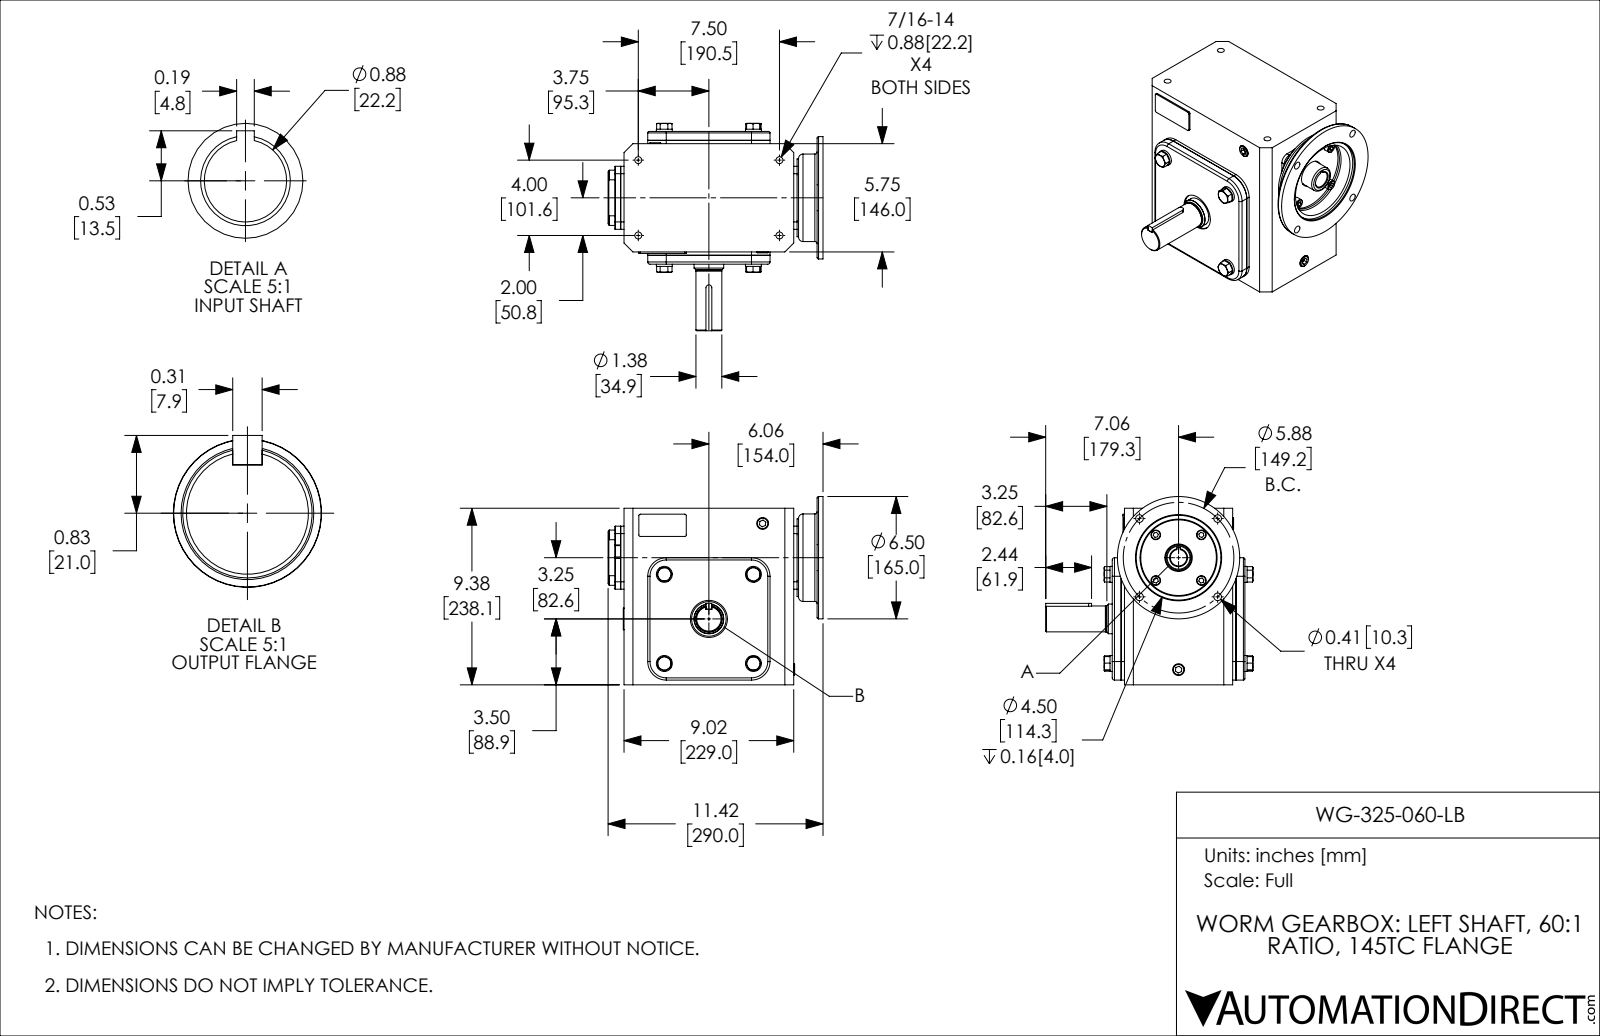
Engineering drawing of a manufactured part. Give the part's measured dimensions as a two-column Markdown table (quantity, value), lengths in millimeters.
| quantity | value |
| --- | --- |
| part name | WG-325-060-LB |
| STEP written by | SolidWorks 2017 (AUTOMOTIVE_DESIGN) |
| units | millimeters |
| bodies | 39 solids, 575 faces (318 planar, 167 cylindrical, 90 other) |
| overall size | 290 × 279.8 × 253.9 |
| volume | 8 259 000 mm³ |
| surface area | 582 200 mm² |
| round holes (diameter × count) | 9.3 × 4, 10.3 × 4, 16 × 3, 15 × 1, 22.2 × 1, 24.8 × 1, 30 × 1, 37 × 1, 50 × 1, 62 × 1, 70 × 1, 102 × 1 |
| round bosses / shafts (diameter × count) | 21.5 × 4, 13 × 4, 165 × 1, 118 × 1, 105 × 1, 72 × 1, 40 × 1, 35 × 1 |
| partial cylindrical surfaces (radius × count) | 2 × 11, 3 × 4, 10 × 4, 23 × 4, 25 × 4, 0.5 × 2, 1 × 2, 4 × 1 |
| main face-to-face distances | 2, 4.5, 165, 10, 177, 12, 167, 162.5, 14.5, 16.5 |
| hole center spacings | 74.6, 105.5, 60.6, 101.6, 111.5, 145.2, 147.8, 149.2 |
